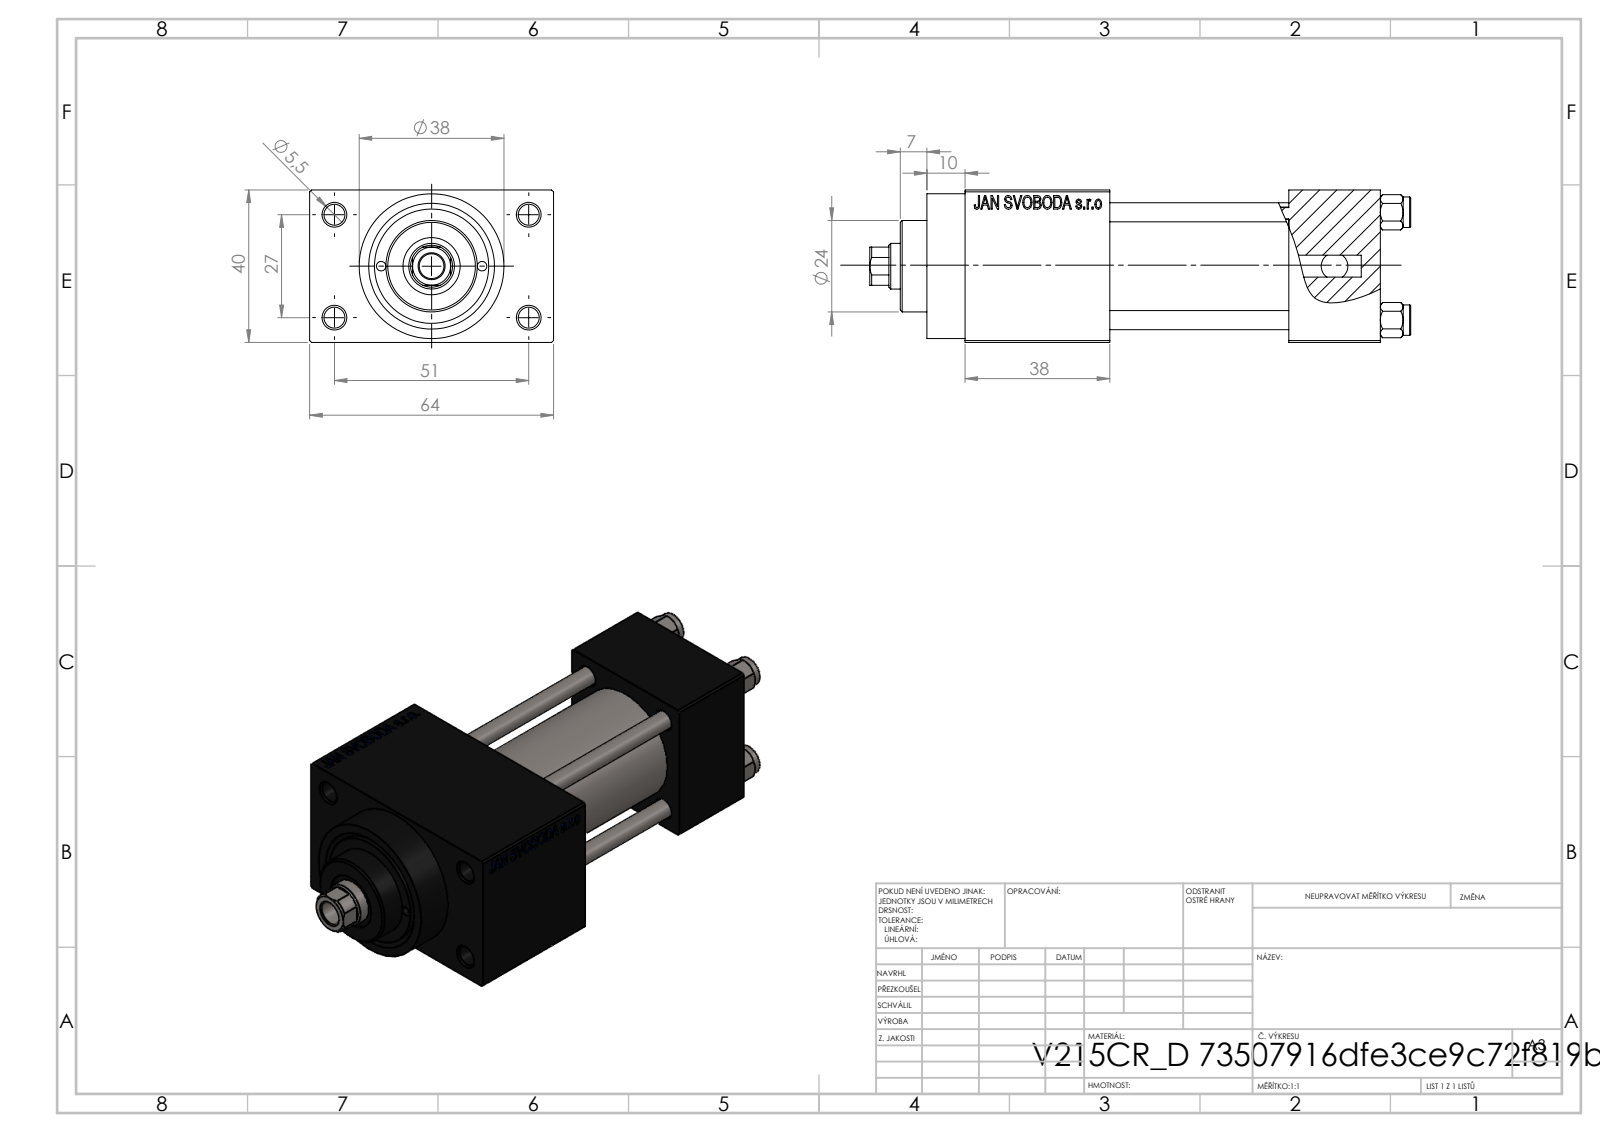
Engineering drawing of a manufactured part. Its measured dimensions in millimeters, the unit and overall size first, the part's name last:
Units: millimetres
Overall size (bounding box): 142 × 64 × 40
Round holes (diameter × count): ⌀5 ×4, ⌀5.5 ×4, ⌀20 ×3, ⌀2.5 ×2, ⌀7 ×2, ⌀13.16 ×2, ⌀6.5 ×1, ⌀12 ×1, ⌀15 ×1, ⌀25 ×1, ⌀30 ×1
Round bosses / shafts (diameter × count): ⌀8 ×4, ⌀38 ×1, ⌀31 ×1, ⌀24 ×1
Partial cylindrical surfaces — rounded edges, fillets, slot ends (radius × count): R5.5 ×1
Main face-to-face distances: 40, 12, 47, 24, 71, 52, 38, 109, 85, 64
Hole centre spacings: 11.37, 14.18, 18.23, 20.01, 28.3, 28.85, 29.89, 30.84
Volume: 173 524 mm³ · Surface area: 62 158 mm²
Bodies: 11 solids, 1110 faces (498 planar, 92 cylindrical, 520 other)
Part name (STEP PRODUCT): NUT_M5_D; V215_VC_A; V215CR_D_TYCINKA; V215CR_D_Body (+1 more)
STEP written by: SolidWorks 2019 (CONFIG_CONTROL_DESIGN)
